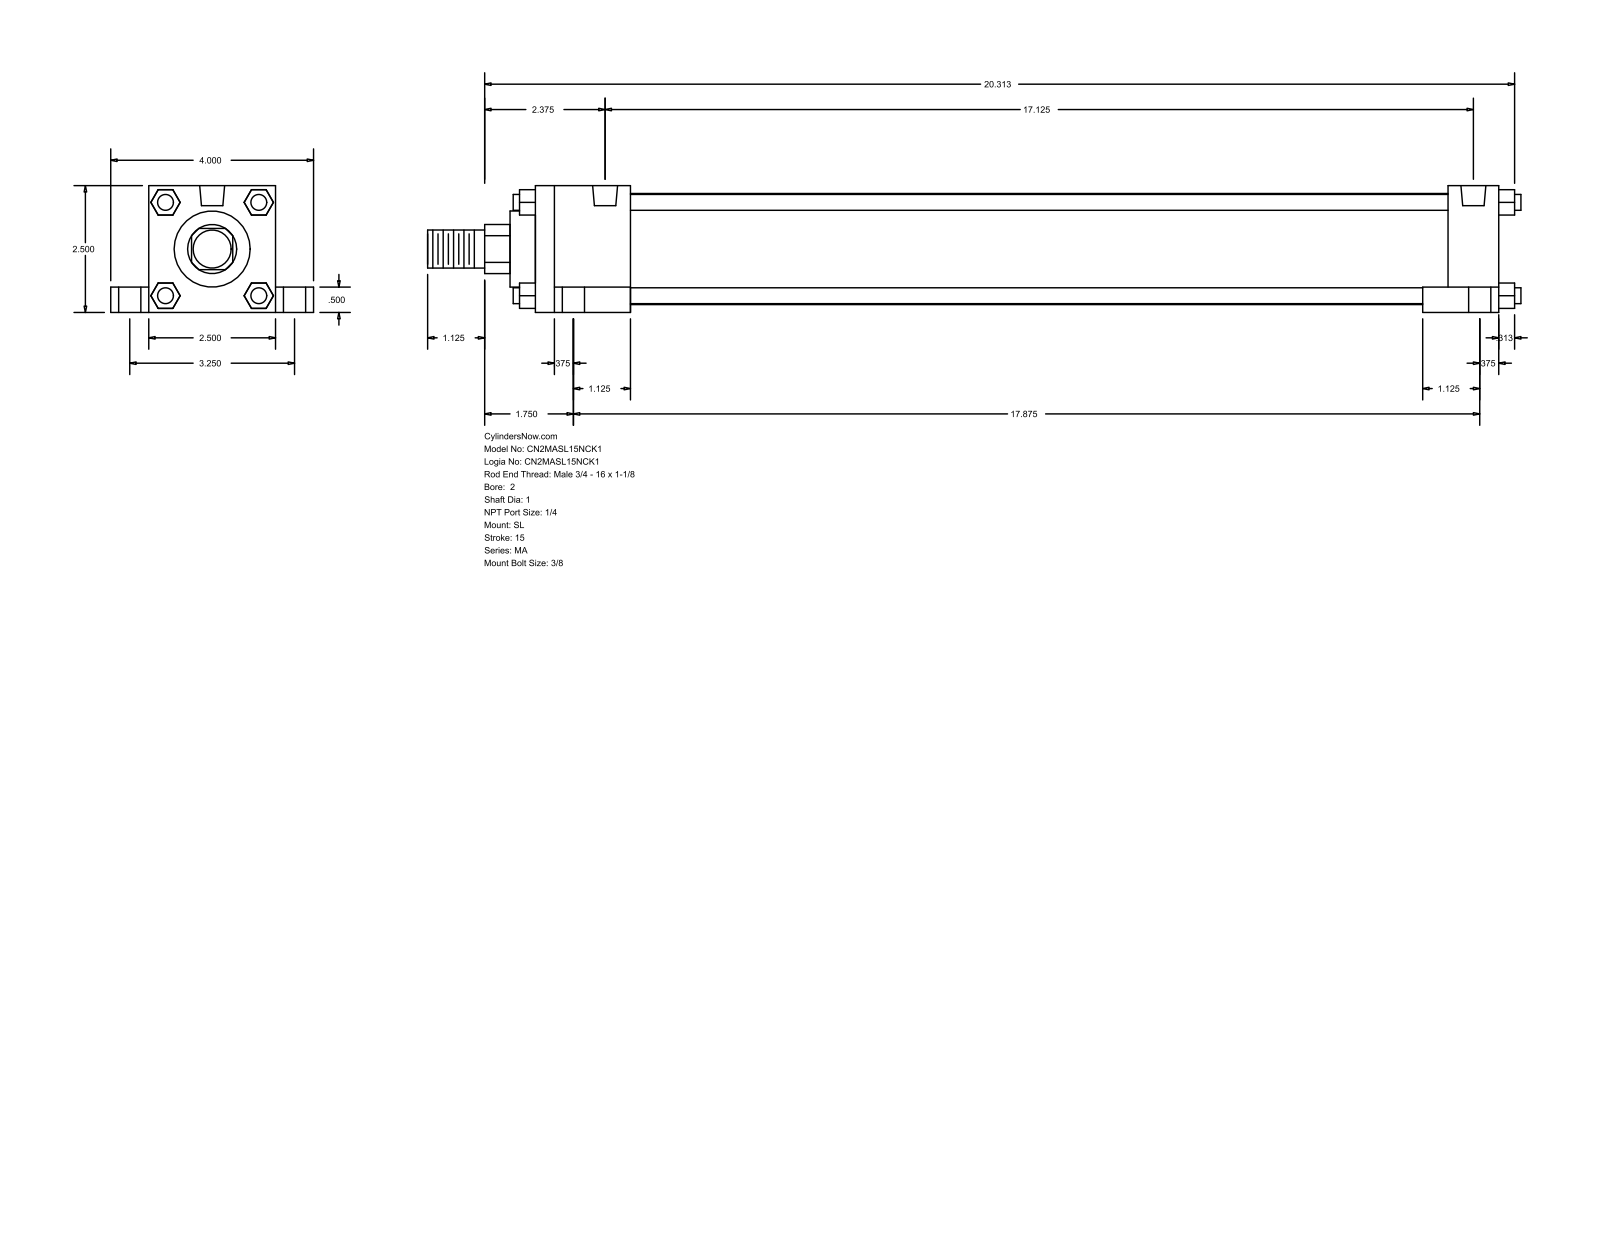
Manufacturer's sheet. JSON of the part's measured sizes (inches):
{"part_name": "MA_SL__0200_1", "step_written_by": "GSSL Pune (CONFIG_CONTROL_DESIGN)", "units": "inches", "bodies": {"solids": 0, "faces": 148, "planar": 112, "cylindrical": 36, "other": 0}, "overall_size": [21.563, 4, 2.5], "round_holes": [[0.313, 4], [0.437, 4], [0.687, 4], [0.492, 2]], "round_bosses_or_shafts": [[0.313, 4], [2.19, 1], [1.5, 1], [1, 1], [0.75, 1]], "partial_cylinders_radius": [[0.484, 1]], "face_to_face_distances": [2.5, 0.5, 19, 0.75, 3.25, 1, 2, 1.875, 17.125, 18], "hole_center_spacings": [1.63, 1.741, 3.25, 17.125, 17.326, 17.824, 17.875, 18.168]}
